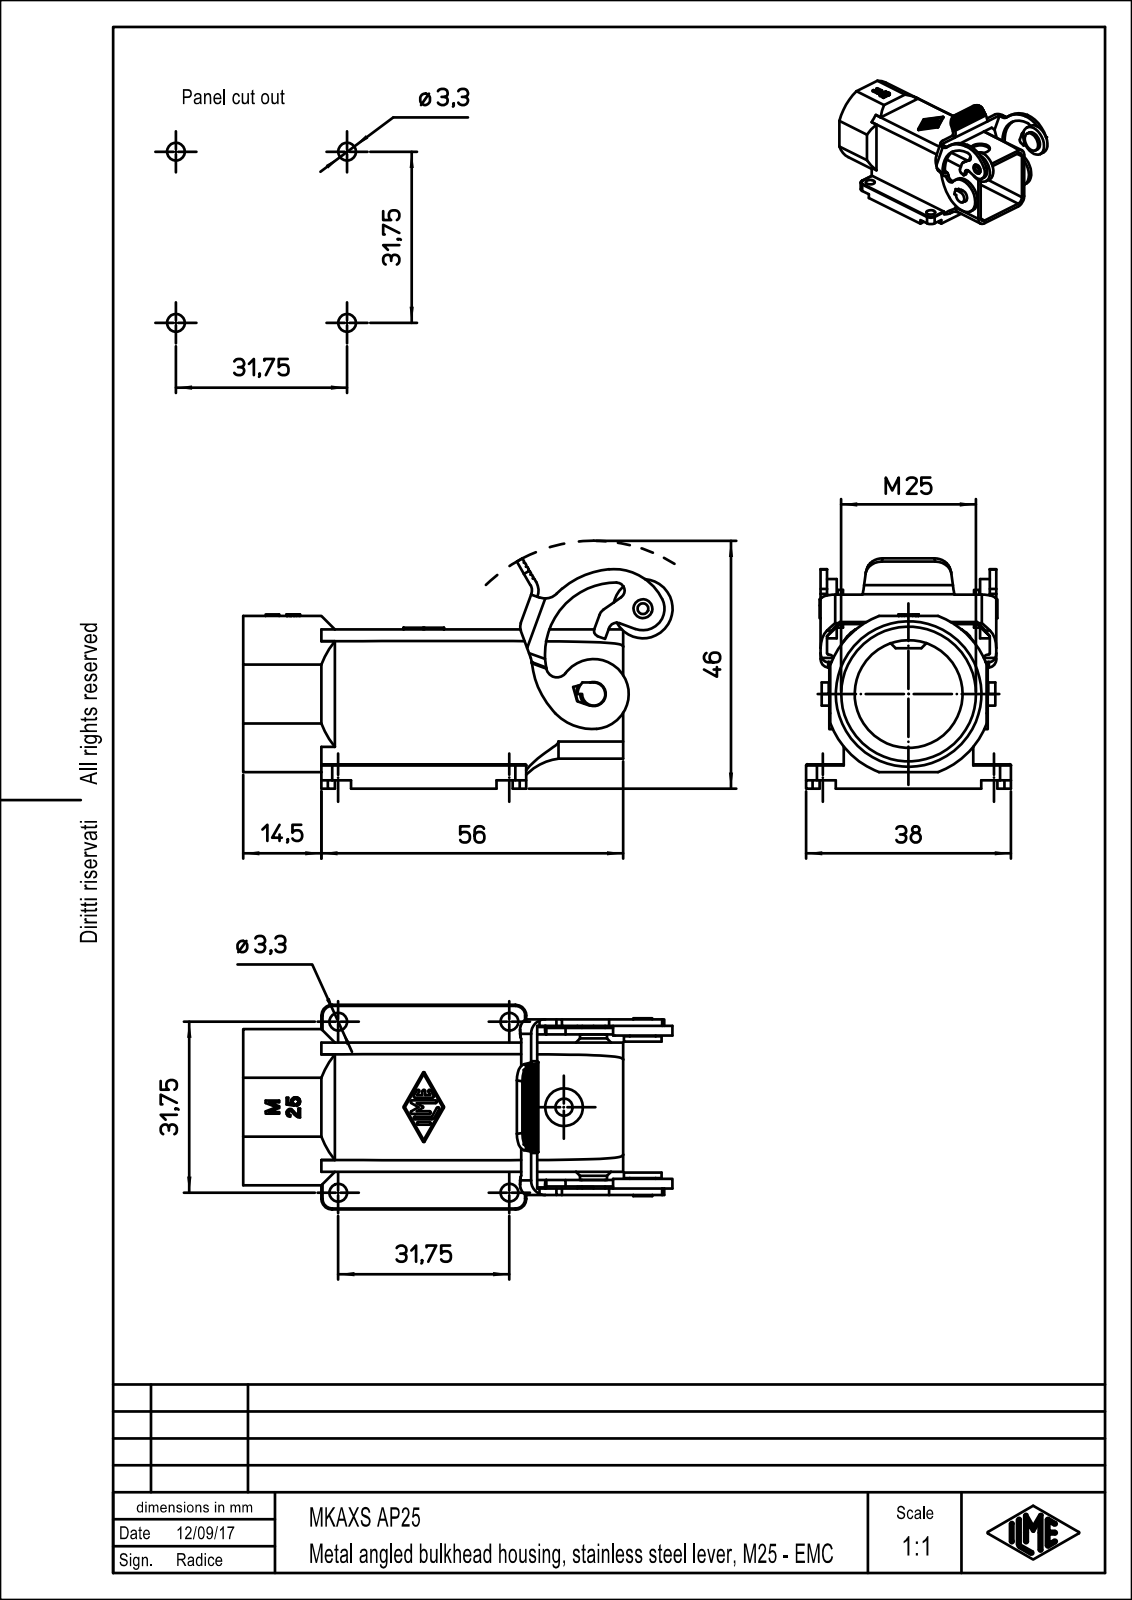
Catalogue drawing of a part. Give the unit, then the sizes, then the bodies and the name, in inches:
Units: inches
Overall size (bounding box): 3.135 × 1.683 × 1.496
Round holes (diameter × count): ⌀0.13 ×4, ⌀0.079 ×1, ⌀0.126 ×1, ⌀0.197 ×1, ⌀0.276 ×1, ⌀0.787 ×1, ⌀0.984 ×1
Round bosses / shafts (diameter × count): ⌀0.433 ×1, ⌀0.276 ×1, ⌀0.197 ×1, ⌀0.189 ×1, ⌀0.169 ×1, ⌀0.138 ×1
Partial cylindrical surfaces — rounded edges, fillets, slot ends (radius × count): R0.079 ×20, R0.01 ×15, R0.008 ×8, R0.126 ×7, R0.118 ×5, R0.055 ×4, R0.005 ×3, R0.059 ×2
Main face-to-face distances: 0.047, 0.898, 0.945, 0.85, 1.102, 0.106, 0.169, 1.173, 0.098, 0.217
Hole centre spacings: 1.25, 1.763, 1.768, 0.741, 0.742
Volume: 1.003 in³ · Surface area: 28.69 in²
Bodies: 1 solid, 470 faces (299 planar, 150 cylindrical, 21 other)
Part name (STEP PRODUCT): MKAXS_AP25
STEP written by: PTC Creo Elements/Direct Modeling 19.0E 27-Jun-2016 (C) Parametric Technology GmbH (AUTOMOTIVE_DESIGN)
